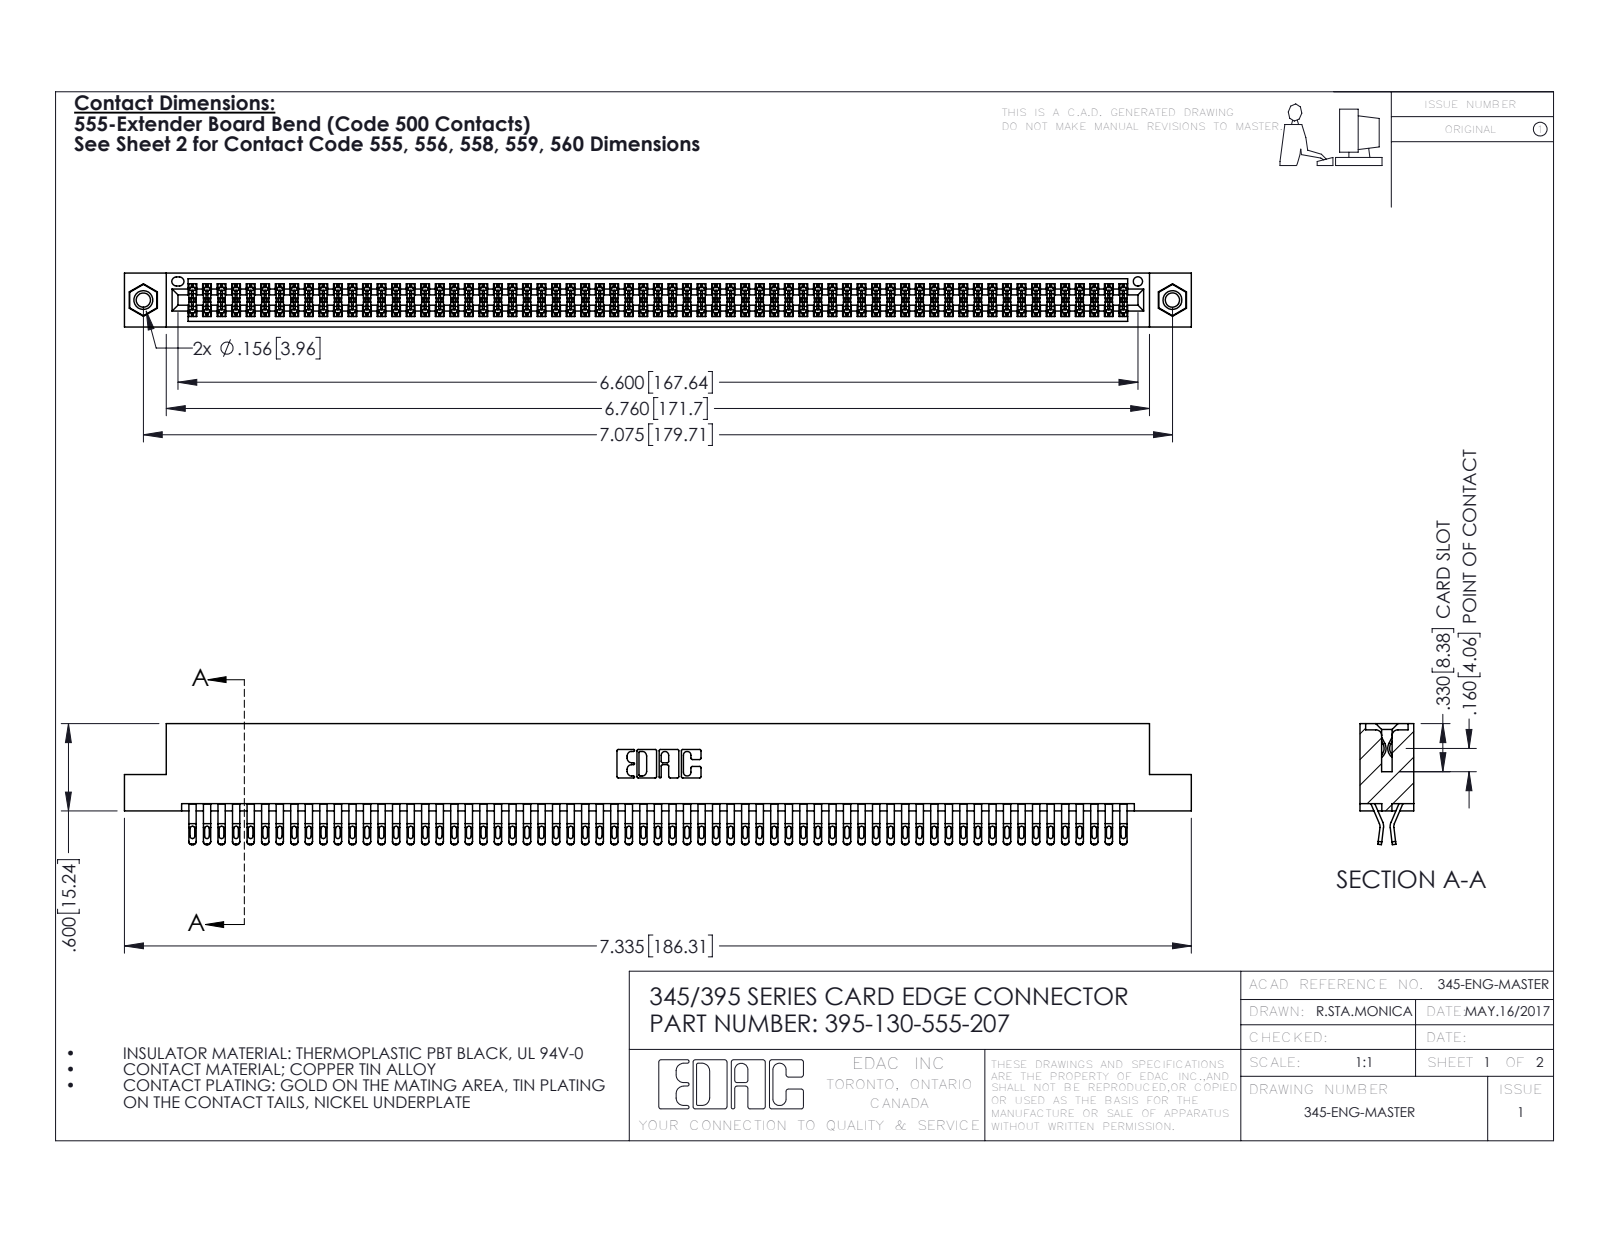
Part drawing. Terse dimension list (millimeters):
name: 395-130-555-207; 345 Part_Flush Mounting Lugs - 0.156 Dia-TI; 345-250-001_345-250-005-103; 345-292-001_555 Tail
written by: SolidWorks 2016 (CONFIG_CONTROL_DESIGN)
unit: mm
bodies: 133 solids, 7466 faces (4142 planar, 3308 cylindrical, 16 other)
size: 186.3 × 21.1 × 9.4
volume: 18 680 mm³; area: 29 390 mm²
holes: 2× ⌀2.5, 2× ⌀3.2, 2× ⌀4, 1× ⌀1.6
bosses: 2× ⌀3.9
rounds: 325× R0.4, 260× R0.5, 195× R0.2, 22× R0.3, 6× R0.2, 6× R0.8, 3× R0.7, 2× R0.3
face distances: 1.8, 7.6, 0.6, 9.4, 5.1, 2.5, 6.9, 5.7, 4.4, 3.8
hole spacings: 6.9, 173.7, 179.7
